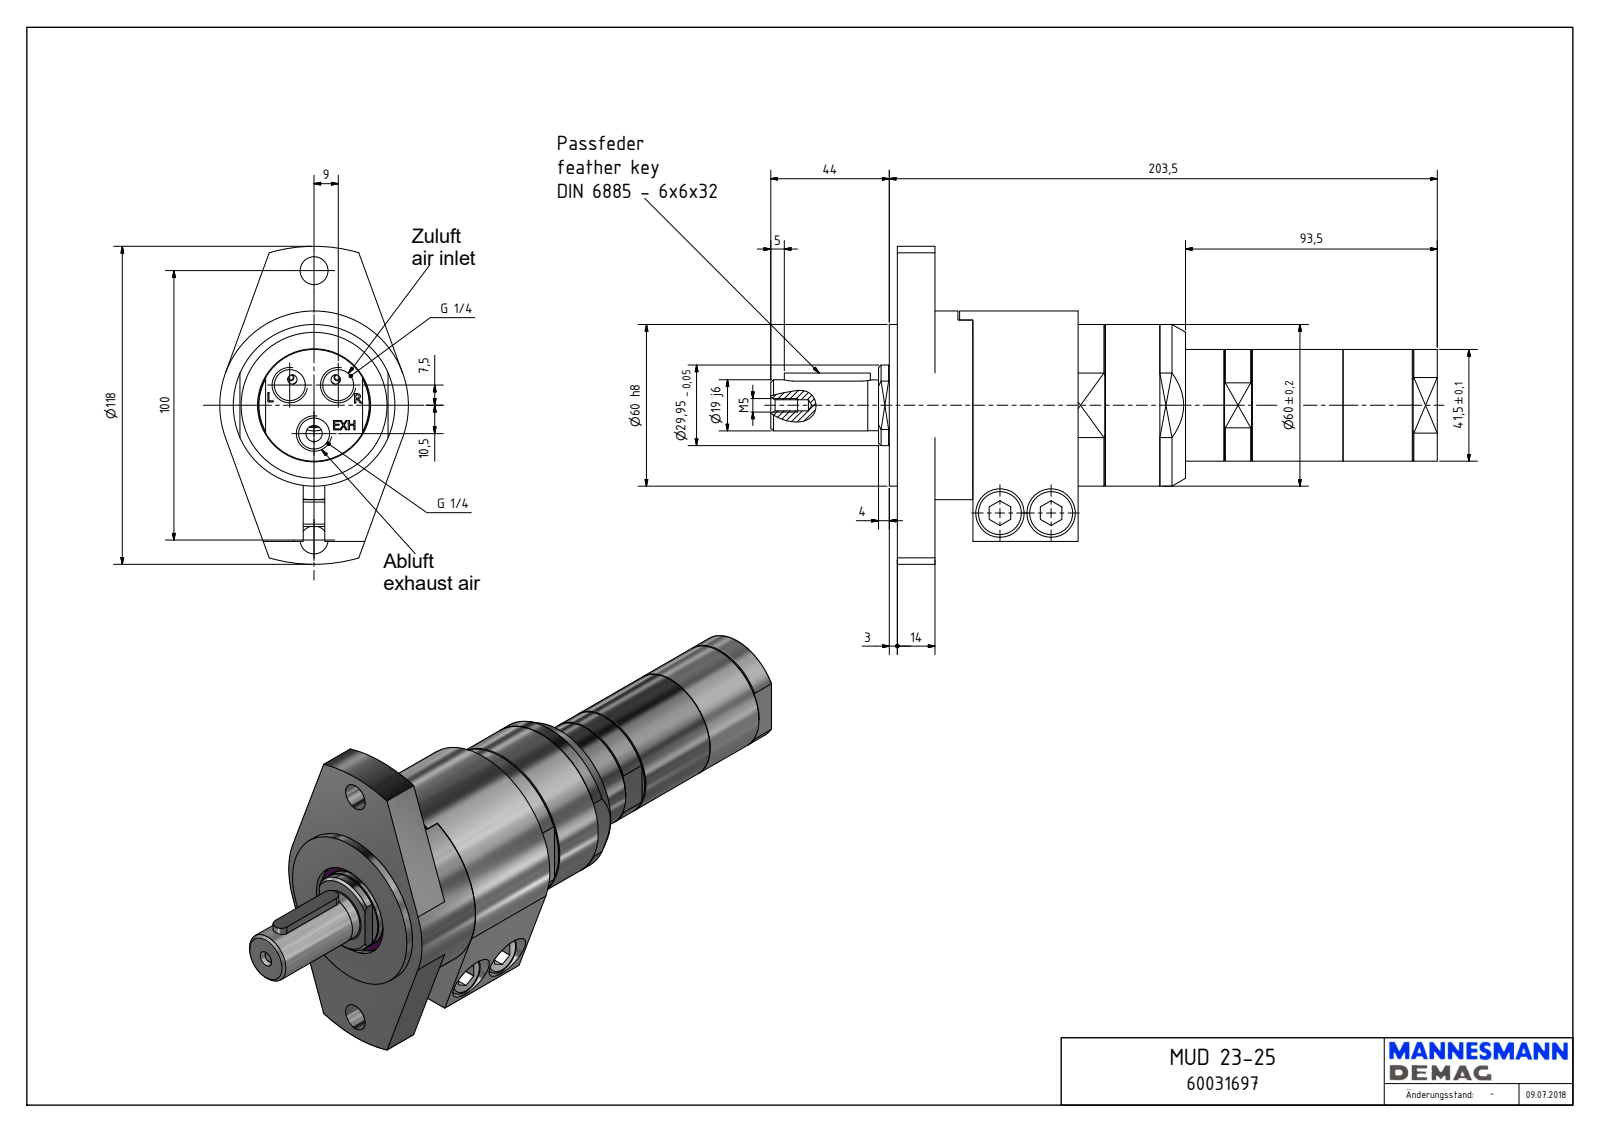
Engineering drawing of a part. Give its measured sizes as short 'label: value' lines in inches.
name: MUD 23-25 F100_60031697
written by: Autodesk Inventor 2018 (AUTOMOTIVE_DESIGN)
unit: in
bodies: 1 solid, 252 faces (148 planar, 56 cylindrical, 48 other)
size: 9.744 × 4.646 × 2.756
volume: 34.62 in³; area: 103.4 in²
holes: 3× ⌀0.451, 2× ⌀0.33, 2× ⌀0.406, 2× ⌀0.413, 2× ⌀0.709, 1× ⌀0.061, 1× ⌀0.157, 1× ⌀0.163, 1× ⌀0.217, 1× ⌀1.378, 1× ⌀1.654
bosses: 2× ⌀0.63, 2× ⌀0.394, 1× ⌀2.756, 1× ⌀2.459, 1× ⌀2.362, 1× ⌀2.172, 1× ⌀1.634, 1× ⌀1.179
rounds: 2× R0.118, 1× R1.067, 1× R2.323
face distances: 0.551, 0.669, 0.118, 2.76, 2.642, 2.091, 1.535, 1.24, 1.224, 1.106
hole spacings: 0.461, 0.792, 1.71, 1.969, 2.291, 0.413, 0.709, 0.748
